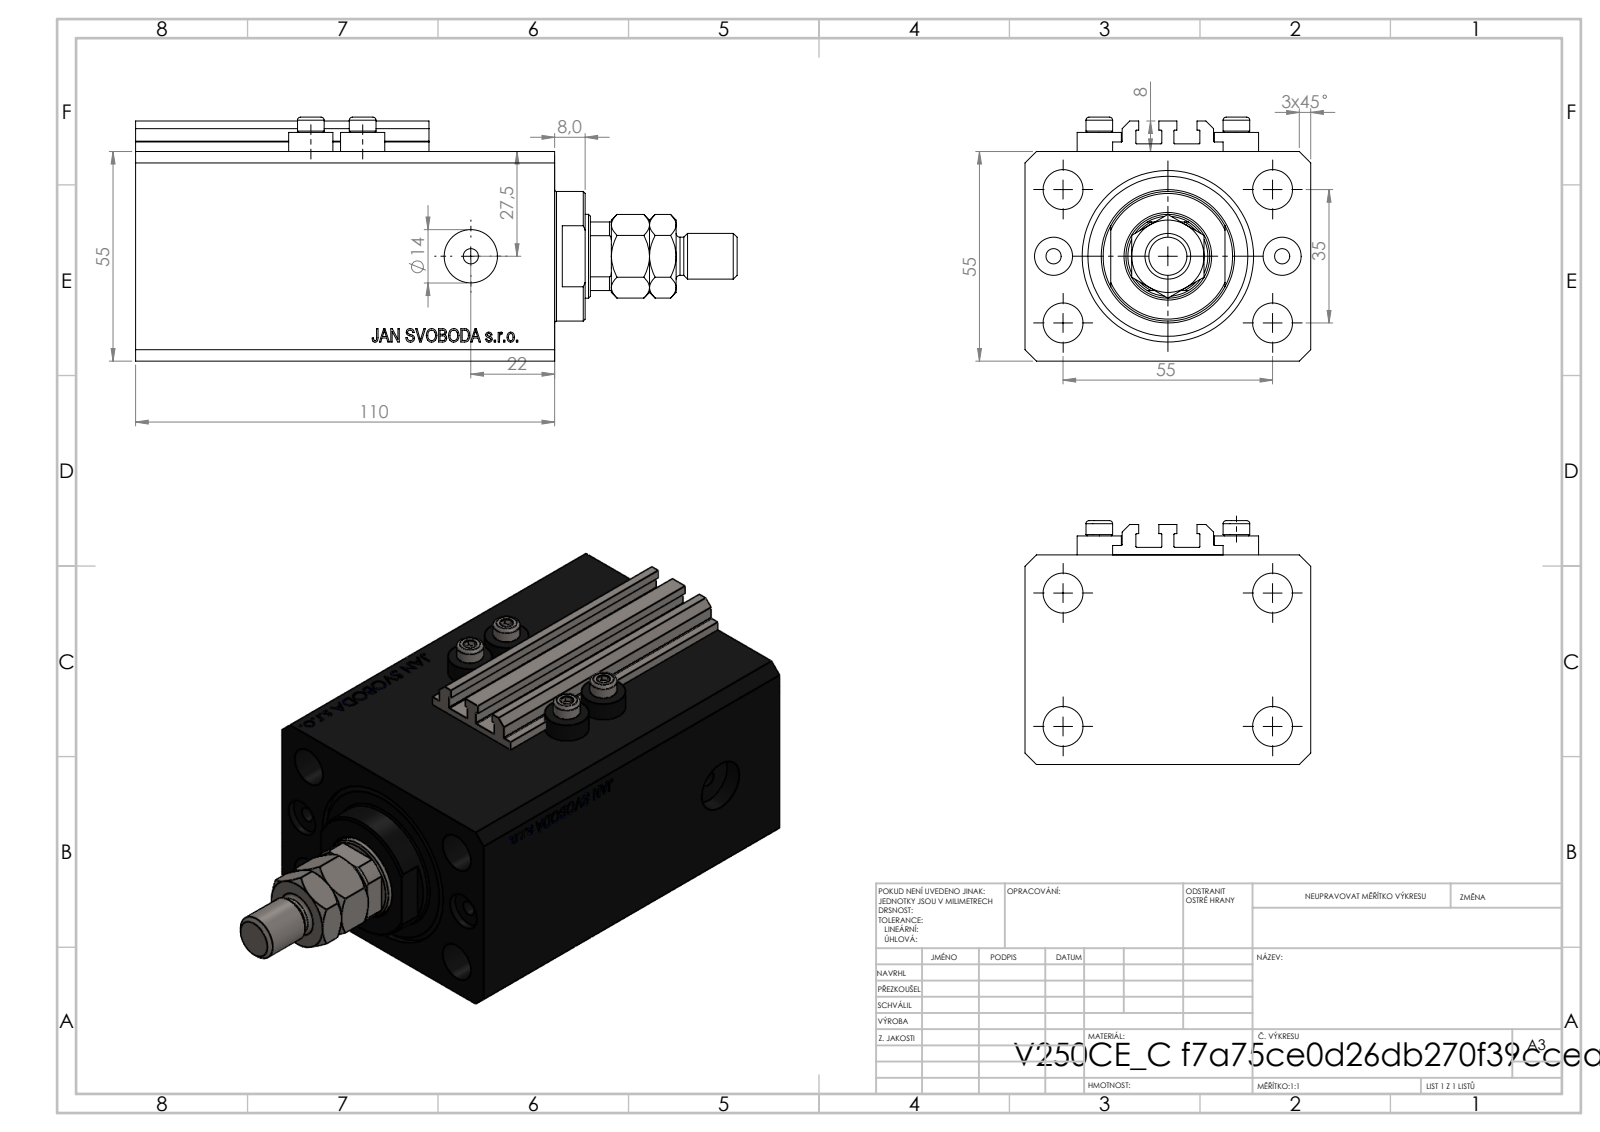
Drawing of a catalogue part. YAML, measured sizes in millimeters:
part_name: "V250CE_C_Body; ALLEN BOLT V250CE; V250CE_C_VCP; MTA (+1 more)"
step_written_by: "SolidWorks 2019 (CONFIG_CONTROL_DESIGN)"
units: millimeters
bodies: {solids: 9, faces: 1082, planar: 518, cylindrical: 90, other: 474}
overall_size: [157.9, 75, 64]
volume: 415843
surface_area: 96090
round_holes:
  - {diameter: 4, count: 8}
  - {diameter: 10.5, count: 5}
  - {diameter: 10, count: 2}
  - {diameter: 14, count: 2}
  - {diameter: 22, count: 1}
  - {diameter: 32, count: 1}
  - {diameter: 45, count: 1}
round_bosses_or_shafts:
  - {diameter: 11.6, count: 4}
  - {diameter: 7, count: 4}
  - {diameter: 34, count: 1}
  - {diameter: 12, count: 1}
  - {diameter: 10, count: 1}
partial_cylinders:
  - {radius: 0.2, count: 10}
  - {radius: 10.5, count: 1}
face_to_face_distances: [55, 75, 110, 82.9, 27.1, 9.9, 73, 100.1, 2.5, 3]
hole_center_spacings: [17.68, 32.6, 60.1, 13.6, 30, 35, 36, 38.48]
